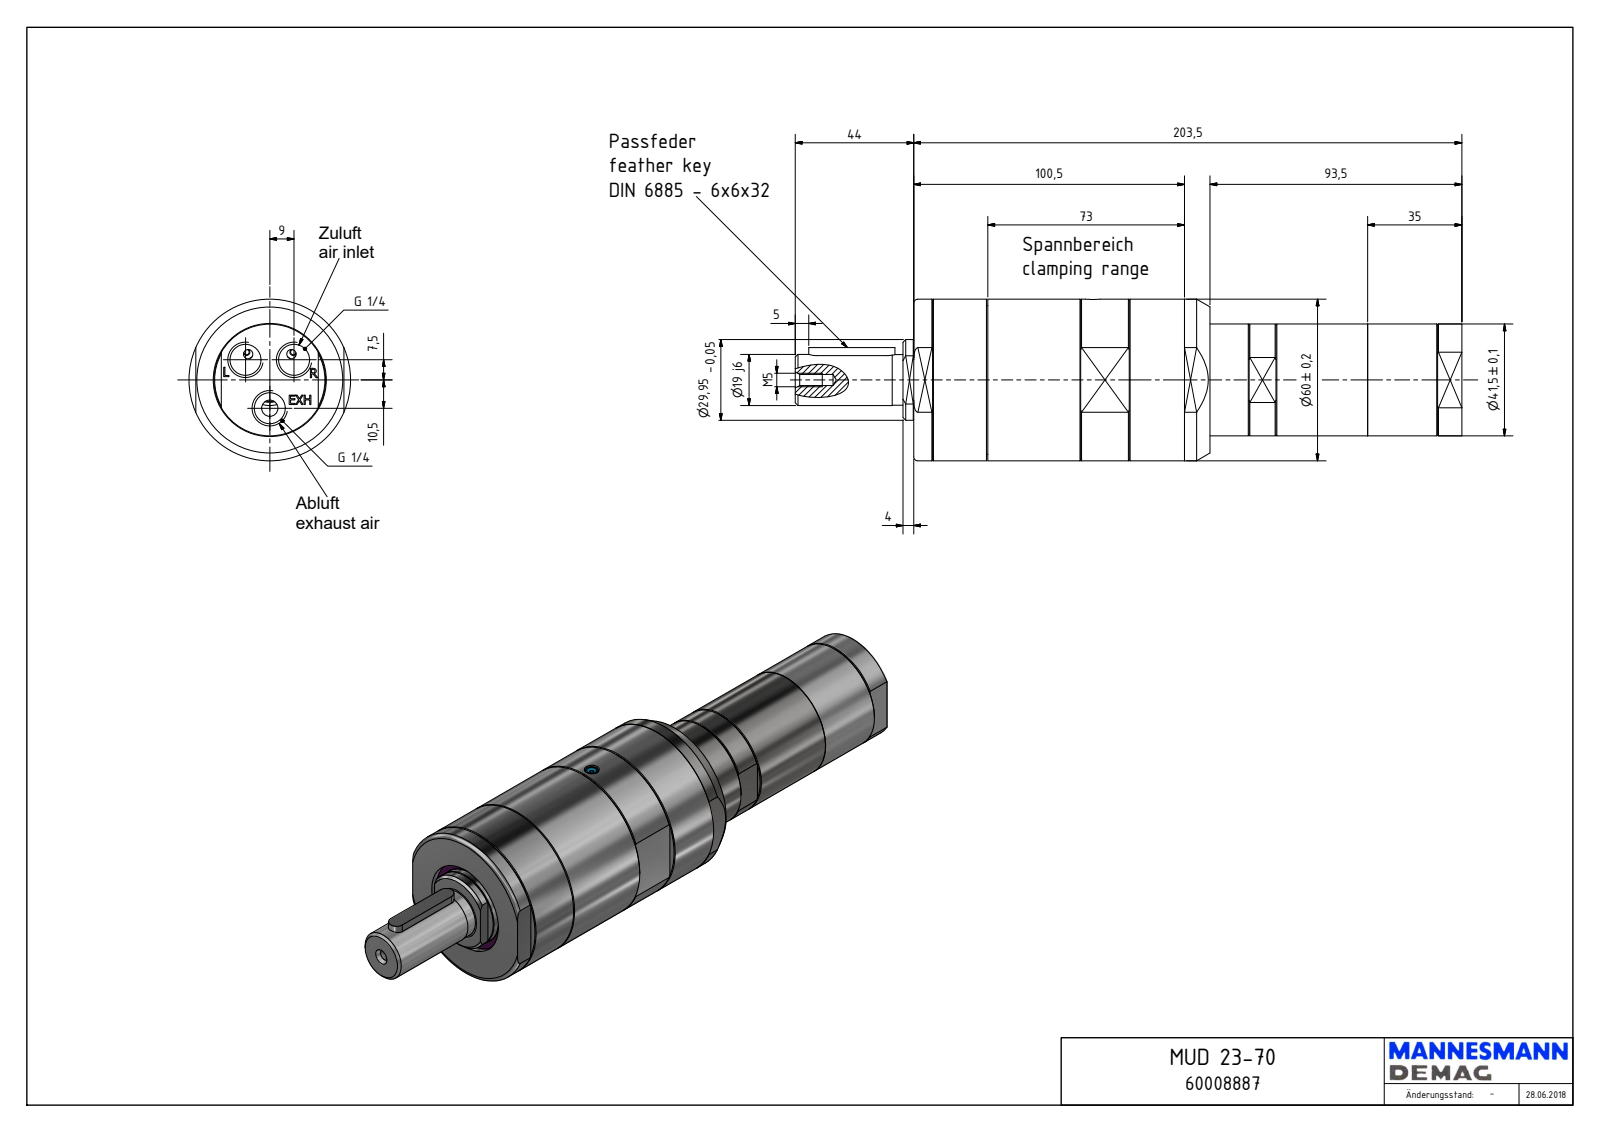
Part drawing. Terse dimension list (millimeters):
name: MUD 23-70_60008887
written by: Autodesk Inventor 2018 (AUTOMOTIVE_DESIGN)
unit: mm
bodies: 1 solid, 474 faces (202 planar, 226 cylindrical, 46 other)
size: 247.5 × 60 × 60
volume: 442 330 mm³; area: 45 948 mm²
holes: 3× ⌀11.45, 1× ⌀1.55, 1× ⌀4, 1× ⌀4.13, 1× ⌀5.5, 1× ⌀35, 1× ⌀42, 1× ⌀55.38
bosses: 1× ⌀60, 1× ⌀55.18, 1× ⌀41.5, 1× ⌀29.95, 1× ⌀19, 1× ⌀18.8, 1× ⌀5, 1× ⌀3.6
rounds: 94× R11.68, 2× R3, 1× R24.71, 1× R24.96, 1× R26.18
face distances: 110, 93.5, 203.5, 55, 83, 9.5, 27.5, 82.5, 176, 31
hole spacings: 11.72, 20.12, 10.5, 18
